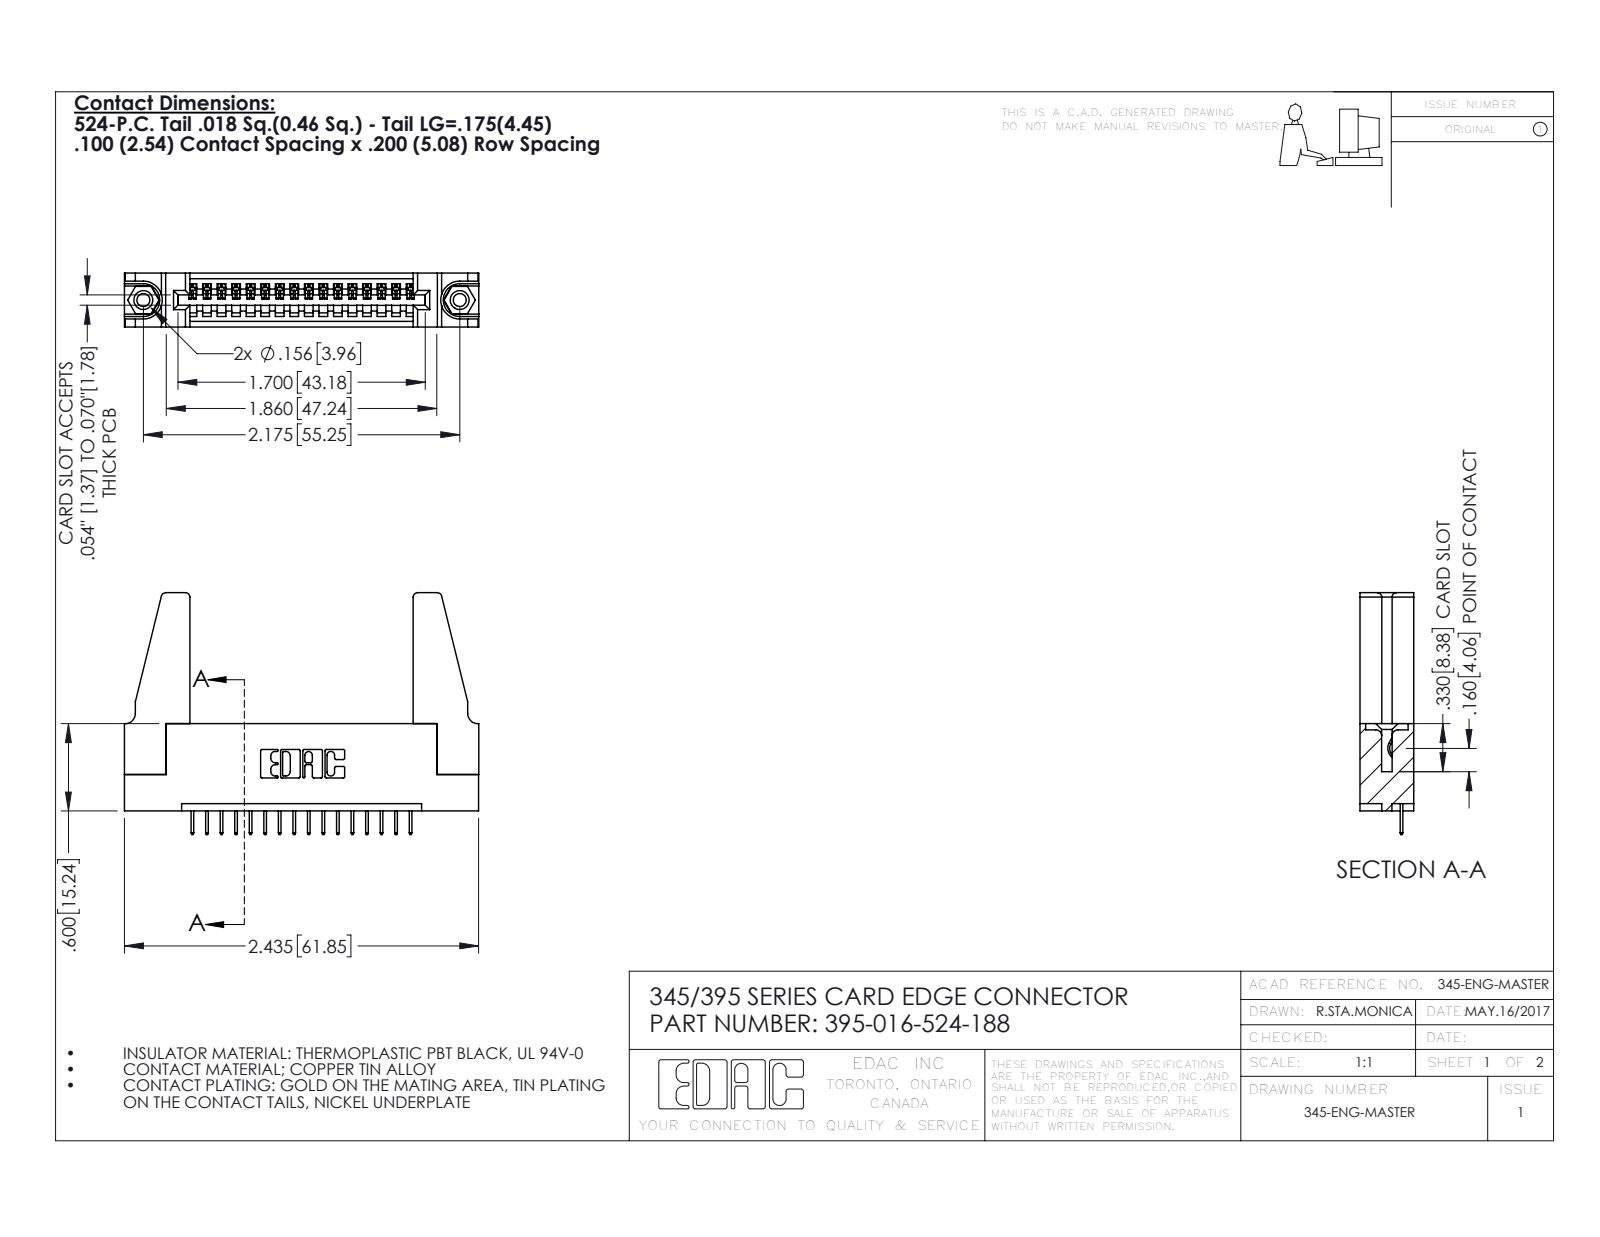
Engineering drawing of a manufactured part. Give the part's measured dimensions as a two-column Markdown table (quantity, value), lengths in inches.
| quantity | value |
| --- | --- |
| part name | 395-016-524-188; 345 Part_Flush Mounting Lugs - 0.156 Dia-TH; 345-250-001_345-250-001-102; 345-292-001_345-293-124 (+1 more) |
| STEP written by | SolidWorks 2016 (CONFIG_CONTROL_DESIGN) |
| units | inches |
| bodies | 21 solids, 1242 faces (888 planar, 338 cylindrical, 16 other) |
| overall size | 2.436 × 1.662 × 0.37 |
| volume | 0.54 in³ |
| surface area | 15.53 in² |
| round holes (diameter × count) | 0.089 × 2, 0.125 × 2, 0.156 × 2, 0.064 × 1 |
| round bosses / shafts (diameter × count) | 0.155 × 2 |
| partial cylindrical surfaces (radius × count) | 0.006 × 32, 0.01 × 22, 0.03 × 8, 0.007 × 6, 0.031 × 6, 0.026 × 3, 0.031 × 2, 0.04 × 2 |
| main face-to-face distances | 0.37, 0.072, 0.298, 0.2, 0.098, 0.272, 0.025, 0.225, 0.148, 0.15 |
| hole center spacings | 0.27, 1.942, 2.175 |
